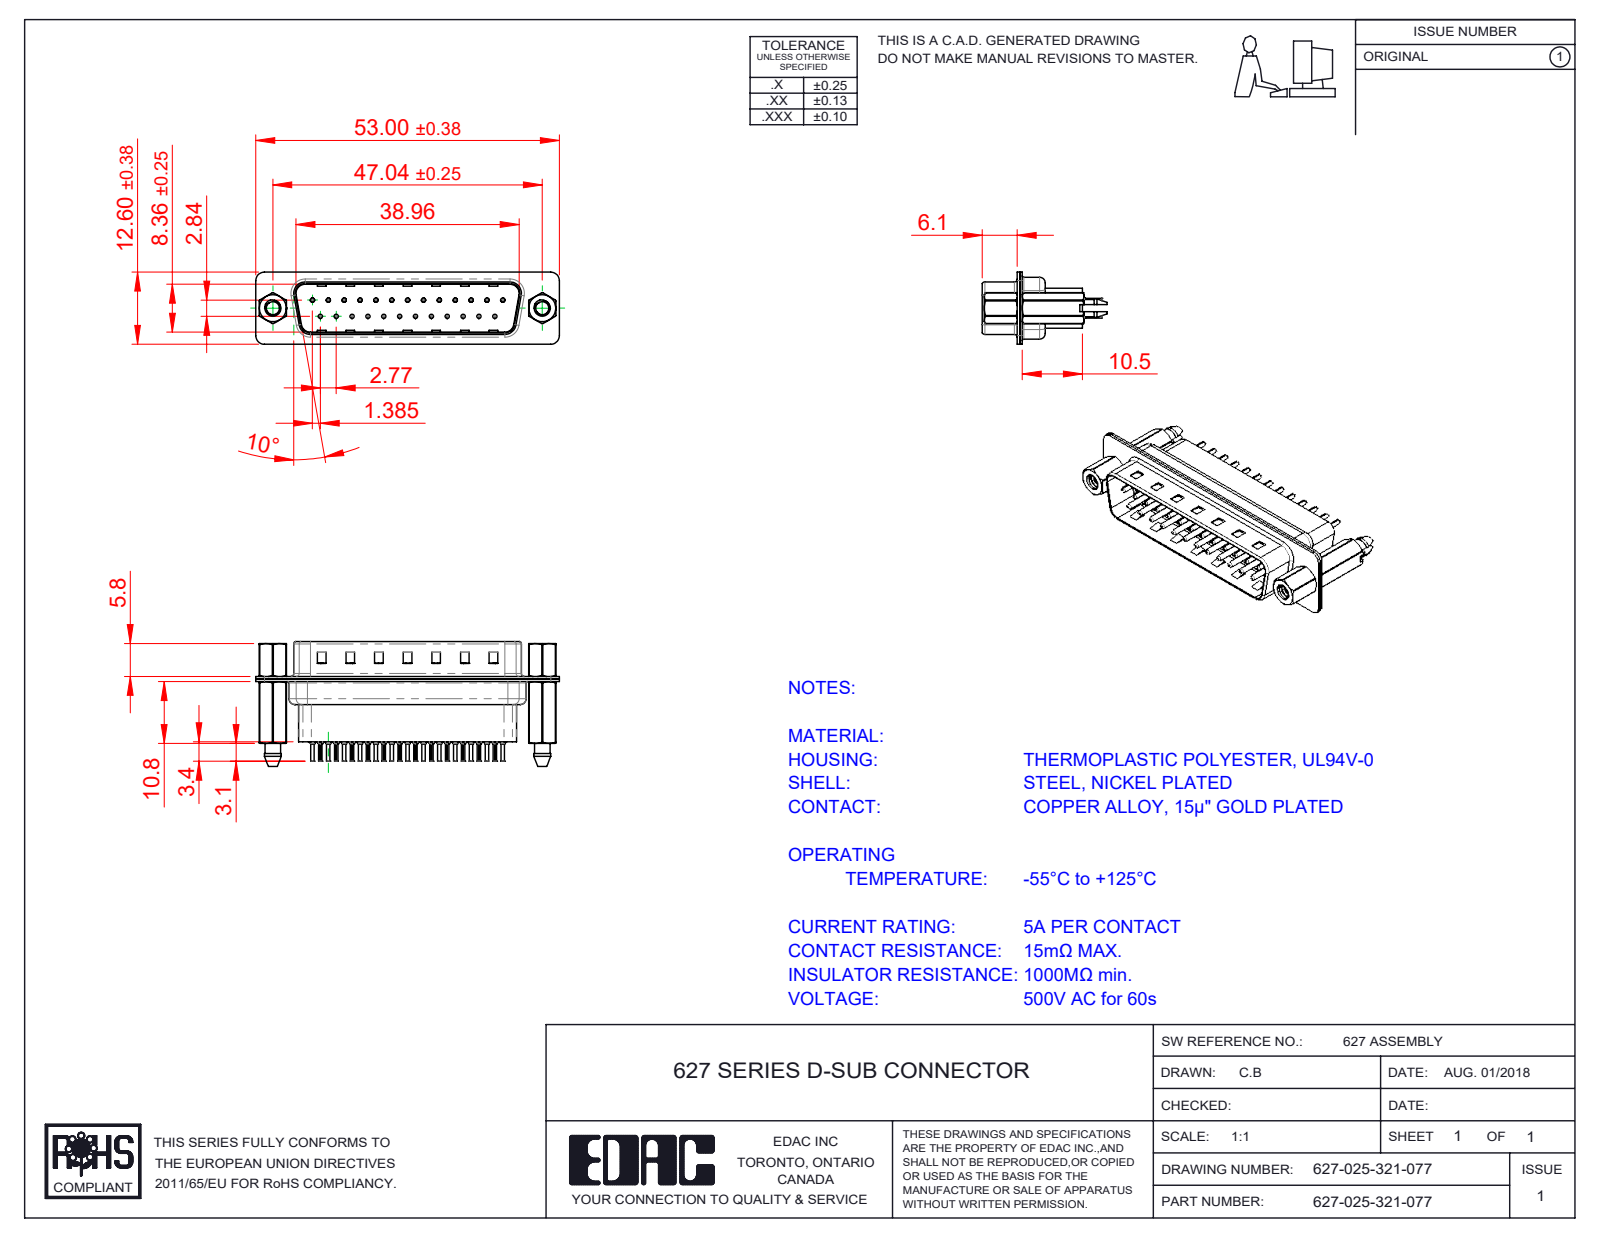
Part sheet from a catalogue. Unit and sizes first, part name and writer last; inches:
Units: inches
Overall size (bounding box): 2.087 × 0.858 × 0.496
Round holes (diameter × count): ⌀0.008 ×25, ⌀0.014 ×25, ⌀0.043 ×25, ⌀0.063 ×25, ⌀0.089 ×2, ⌀0.09 ×2, ⌀0.157 ×2, ⌀0.189 ×2
Round bosses / shafts (diameter × count): ⌀0.079 ×25, ⌀0.059 ×25, ⌀0.03 ×25, ⌀0.024 ×25, ⌀0.193 ×2, ⌀0.11 ×2
Partial cylindrical surfaces — rounded edges, fillets, slot ends (radius × count): R0.004 ×50, R0.059 ×18, R0.079 ×12, R0.063 ×10, R0.02 ×8, R0.01 ×4, R0.024 ×4, R0.026 ×4
Main face-to-face distances: 0.016, 0.018, 0.032, 0.377, 0.027, 0.302, 0.059, 0.043, 0.318, 0.345
Hole centre spacings: 0.124, 0.109, 0.218, 0.327, 0.436, 0.545, 0.198, 0.295
Volume: 0.26 in³ · Surface area: 16.83 in²
Bodies: 32 solids, 3066 faces (825 planar, 1202 cylindrical, 1039 other)
Part name (STEP PRODUCT): 627 4-40 Threaded Boardlock_HP; 627 Shell Front_25 Contacts; 627-025-321-077; 627 4-40 Hex Standoff (+4 more)
STEP written by: SolidWorks 2020 (CONFIG_CONTROL_DESIGN)
